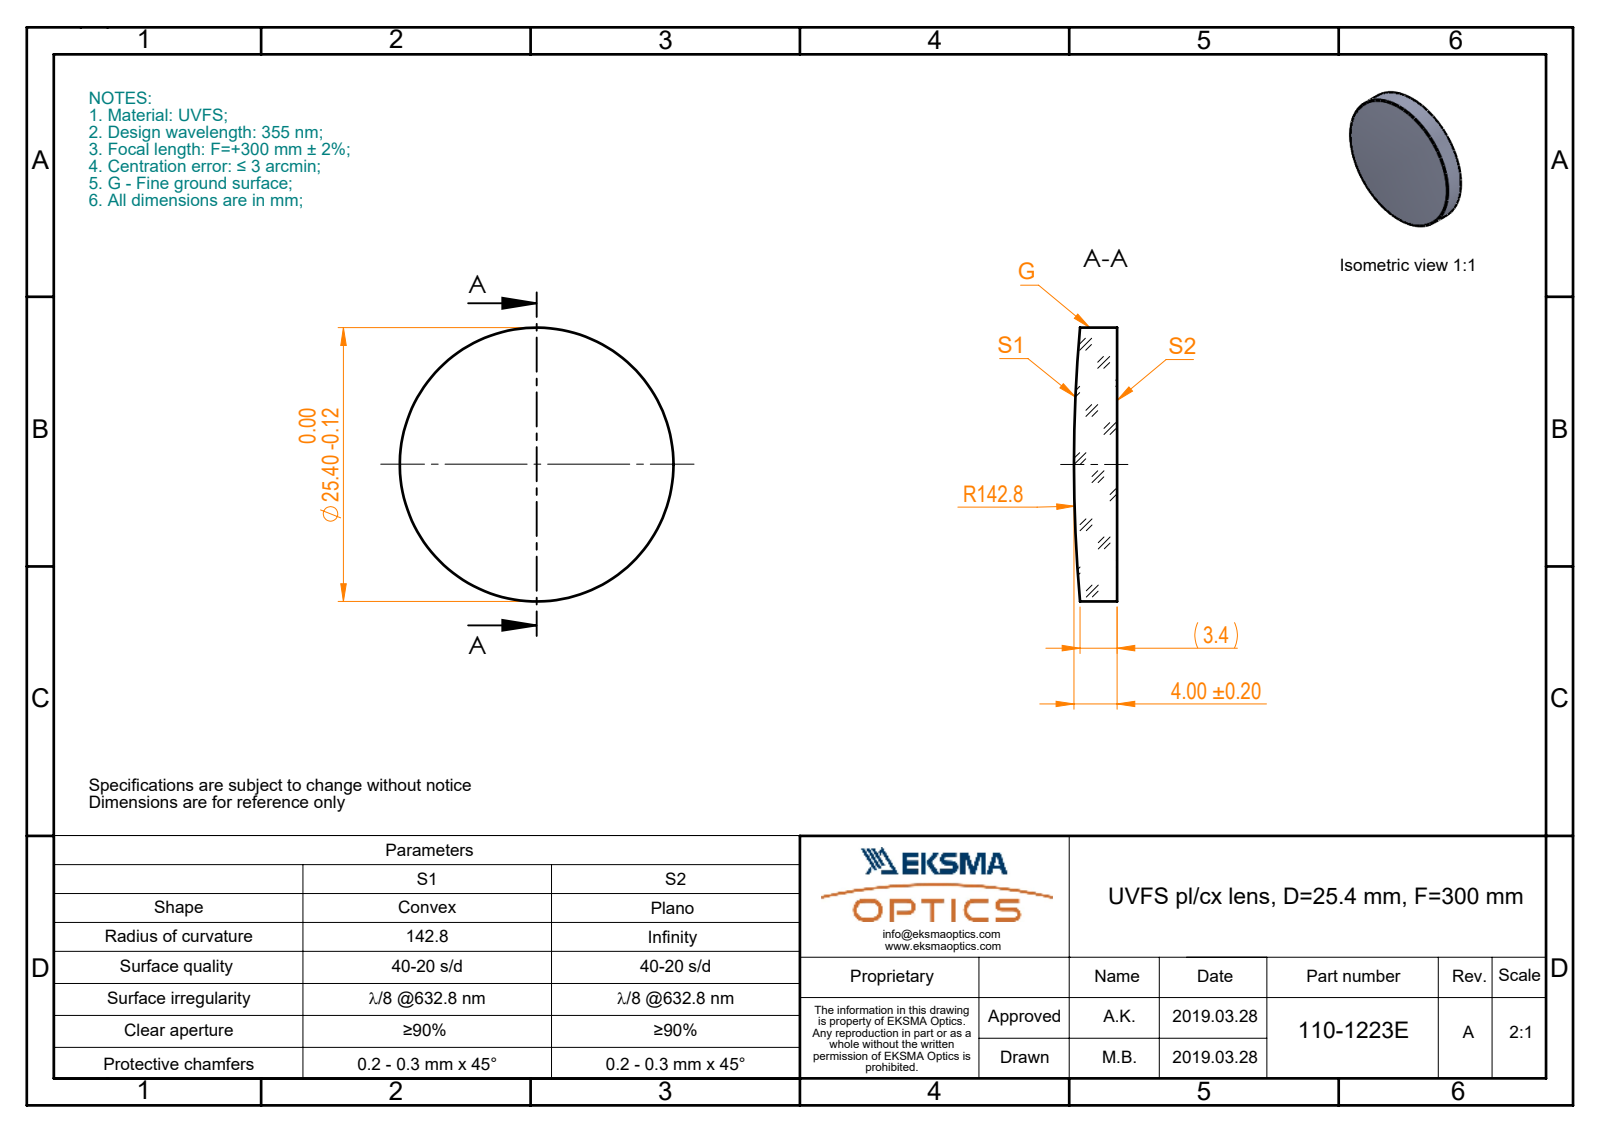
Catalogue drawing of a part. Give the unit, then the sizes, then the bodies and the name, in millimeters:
Units: millimetres
Overall size (bounding box): 25.4 × 25.4 × 4
Round bosses / shafts (diameter × count): ⌀25.4 ×1
Volume: 1 884 mm³ · Surface area: 1 288 mm²
Bodies: 1 solid, 5 faces (1 planar, 2 cylindrical, 2 other)
Part name (STEP PRODUCT): 110-1223E UVFS pl-cx 25.4 F300
STEP written by: SolidWorks 2017 (CONFIG_CONTROL_DESIGN)
